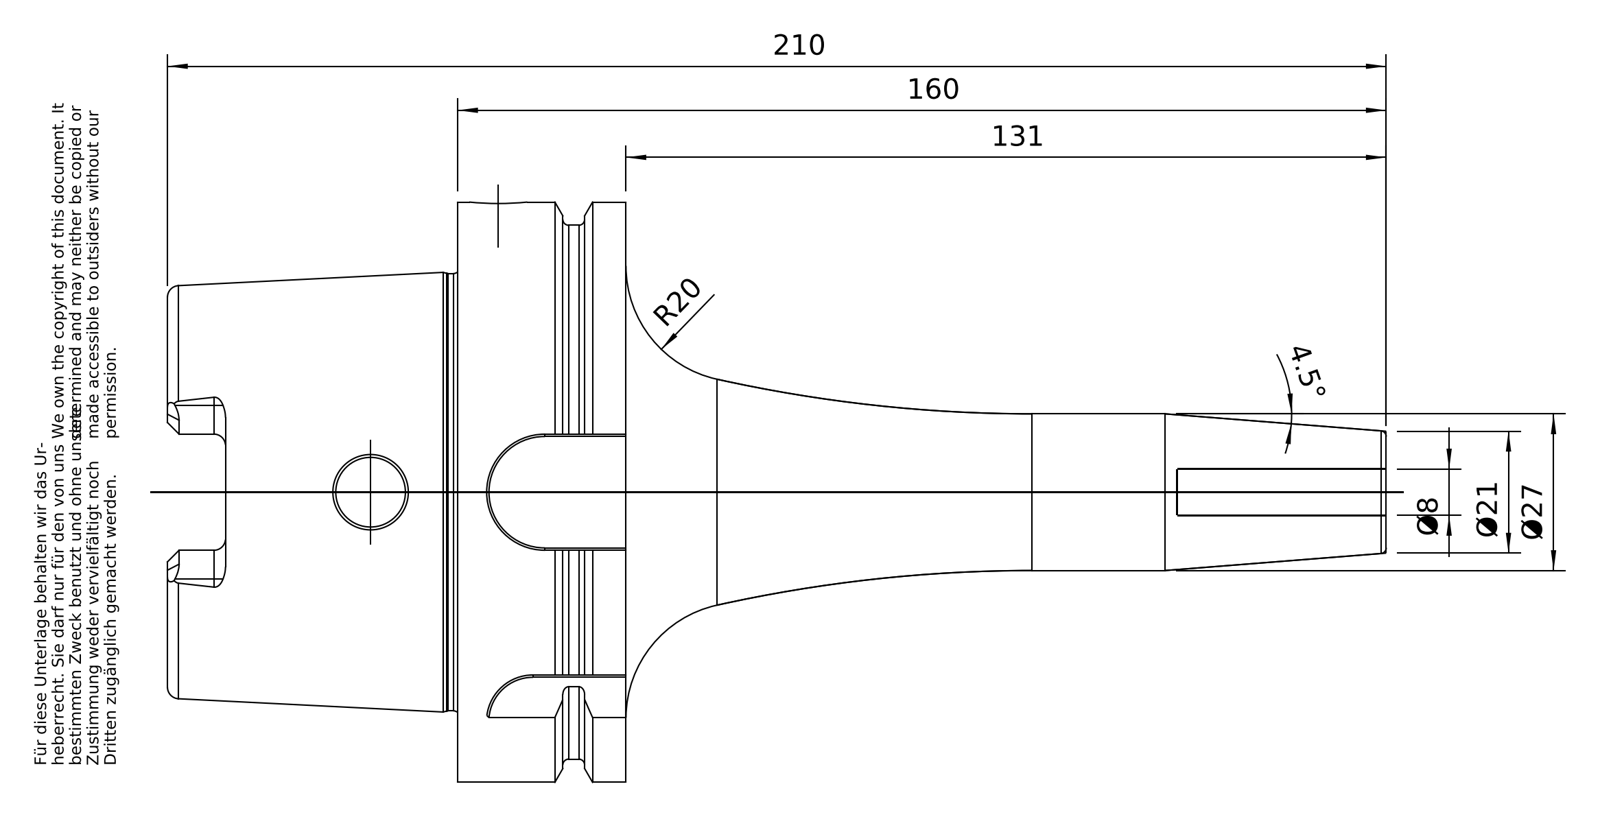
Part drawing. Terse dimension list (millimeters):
name: A100-142-08
written by: PRO/ENGINEER BY PARAMETRIC TECHNOLOGY CORPORATION, 2010430 (CONFIG_CONTROL_DESIGN)
unit: mm
bodies: 1 solid, 176 faces (50 planar, 51 cylindrical, 75 other)
size: 210 × 100 × 100
volume: 354 623 mm³; area: 61 501 mm²
holes: 1× ⌀8, 1× ⌀10, 1× ⌀12, 1× ⌀22.5, 1× ⌀24, 1× ⌀24.32, 1× ⌀24.5, 1× ⌀53, 1× ⌀63
bosses: 1× ⌀100, 1× ⌀92, 1× ⌀75.36, 1× ⌀27
rounds: 6× R2, 4× R5, 1× R8, 1× R10, 1× R11
face distances: 29, 12.5, 16.5, 50, 62.5, 79, 88, 78.5, 28.5, 16
